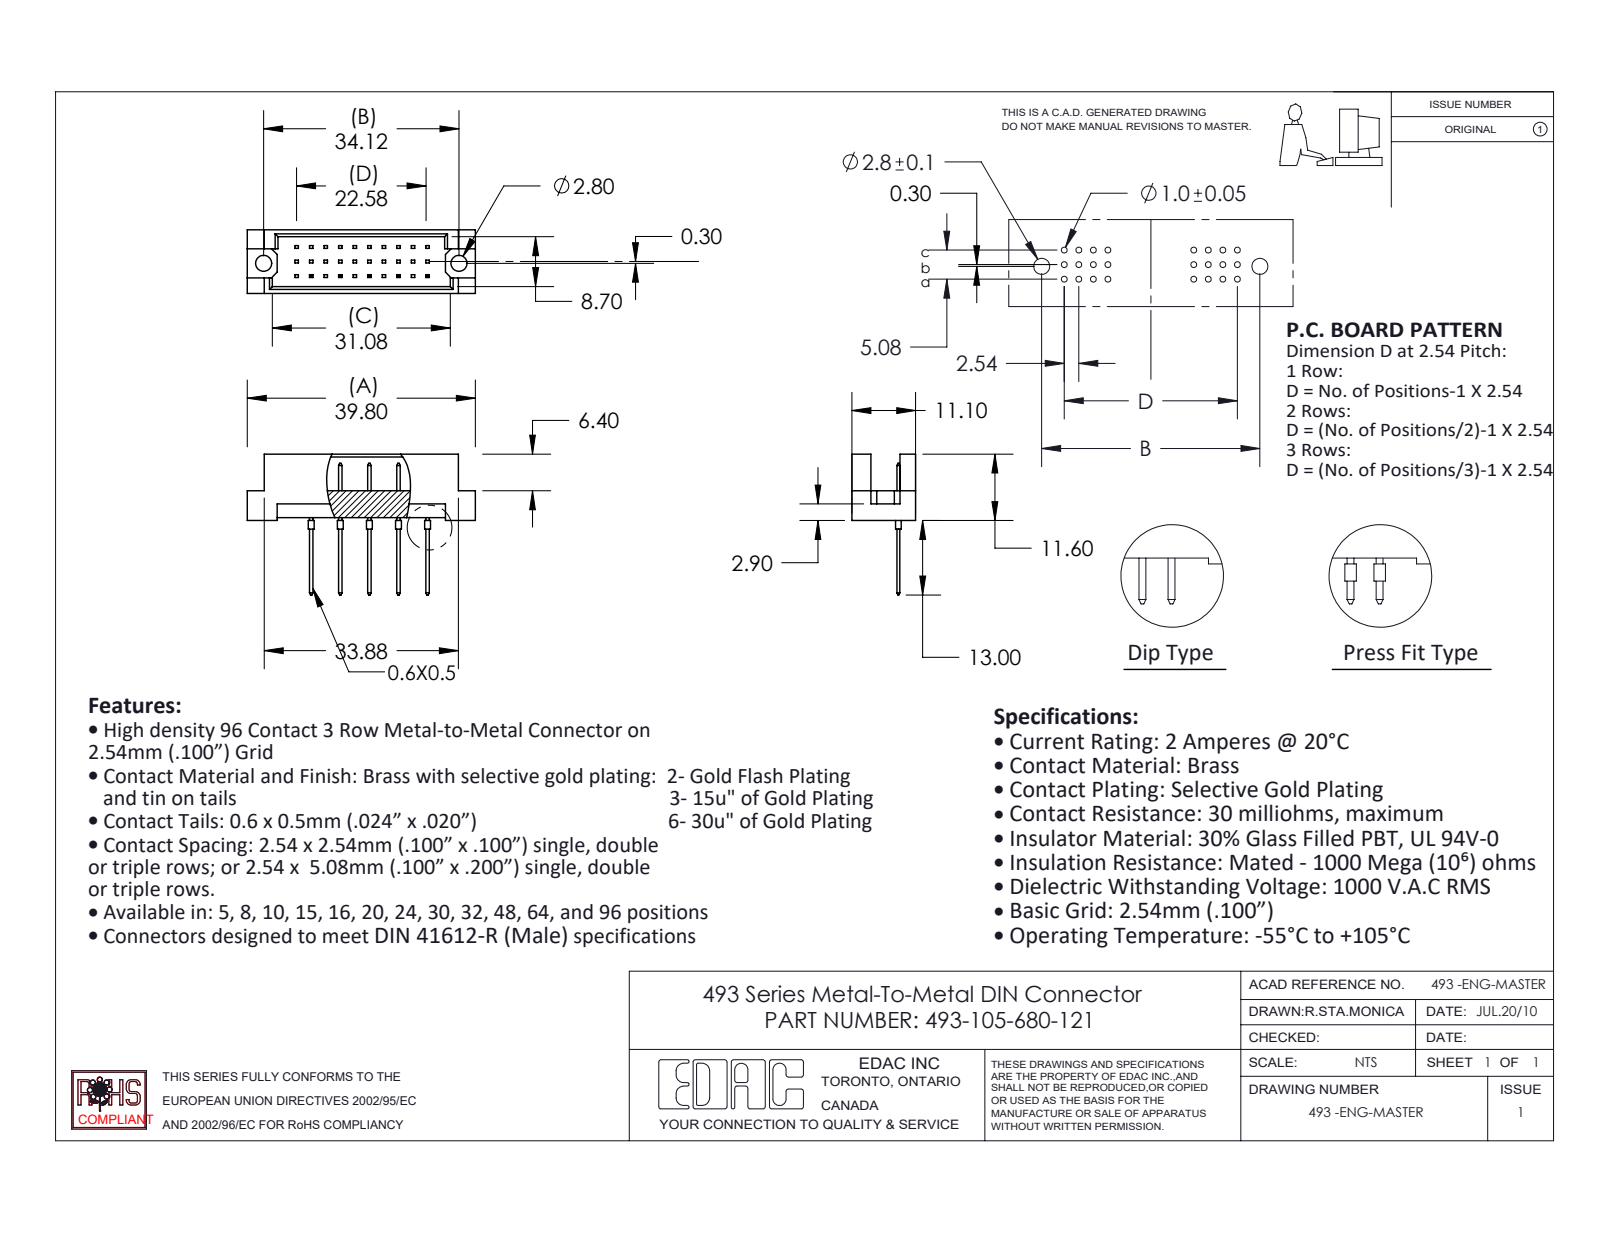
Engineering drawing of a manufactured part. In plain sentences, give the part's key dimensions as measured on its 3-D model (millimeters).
The part is named "493-105-680-121; 493-290_80; 493 Part_30". Its 3-D file was written by "SolidWorks 2020 (CONFIG_CONTROL_DESIGN)". It is 6 solids with 282 faces: 268 planar, 14 cylindrical and 0 other. Overall it measures 39.8 by 24.6 by 11.1 millimeters. Its volume is 2 411 cubic millimeters and its surface area 3 001 square millimeters. Round holes: 2 of diameter 2.8. Round bosses or shafts: 5 of diameter 1. The main face-to-face distances are 1.2, 9.9, 11.1, 8.7, 0.5, 4.7, 5.08, 2.4, 2.76, 3.26. The hole center spacings are 34.12.
